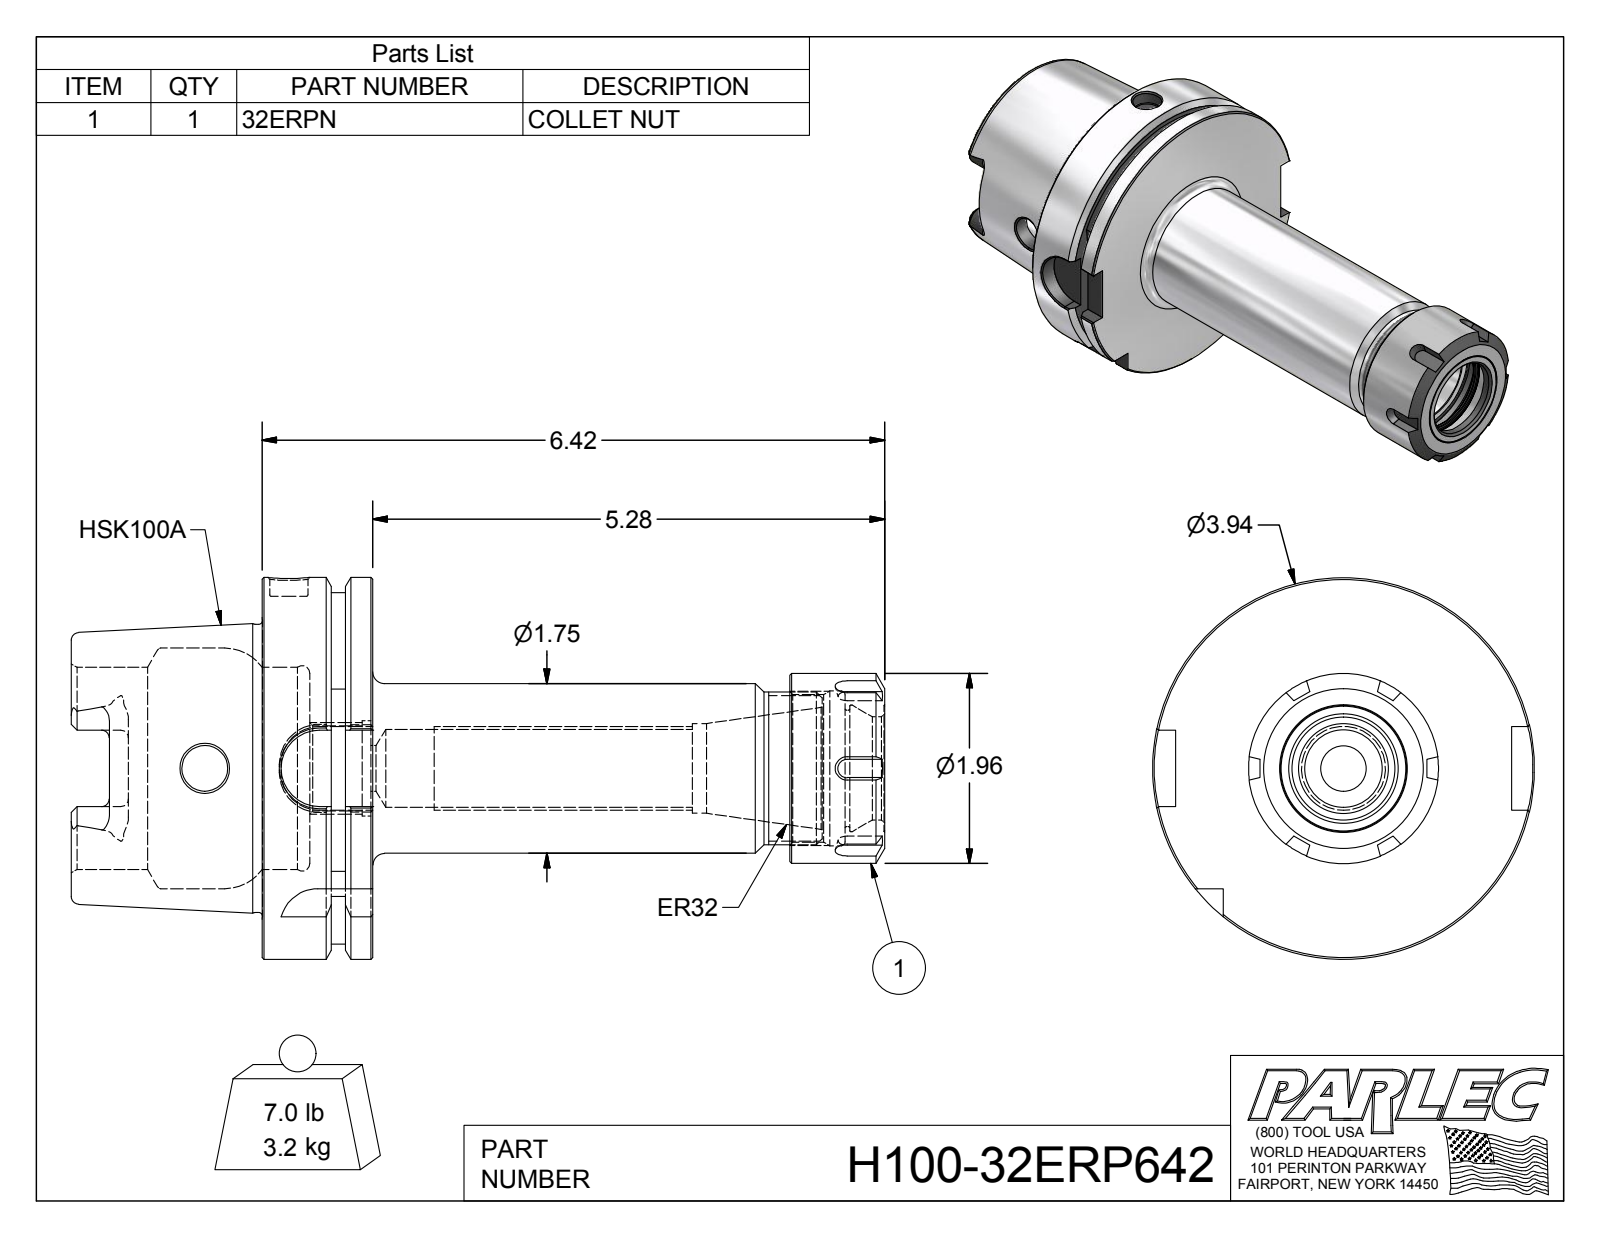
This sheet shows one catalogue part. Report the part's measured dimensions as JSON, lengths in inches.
{"part_name": "H100-32ERP642; H100-32ER630-1; 32ERPN", "step_written_by": "Autodesk Inventor 2012 (AUTOMOTIVE_DESIGN)", "units": "inches", "bodies": {"solids": 2, "faces": 176, "planar": 66, "cylindrical": 41, "other": 69}, "overall_size": [8.389, 3.937, 3.937], "volume_in3": 24.82, "surface_area_in2": 128.2, "round_holes": [[0.472, 2], [0.394, 1], [0.802, 1], [0.881, 1], [0.925, 1], [0.985, 1], [1.063, 1], [1.2, 1], [1.305, 1], [1.523, 1], [1.595, 1], [2.087, 1]], "round_bosses_or_shafts": [[3.937, 1], [2.967, 1], [1.958, 1], [1.75, 1], [1.575, 1]], "partial_cylinders_radius": [[0.079, 6], [0.192, 4], [0.394, 4], [1.811, 1]], "face_to_face_distances": [1.142, 0.492, 0.65, 1.969, 2.461, 3.11, 8.389, 6.42, 5.928, 5.278]}
